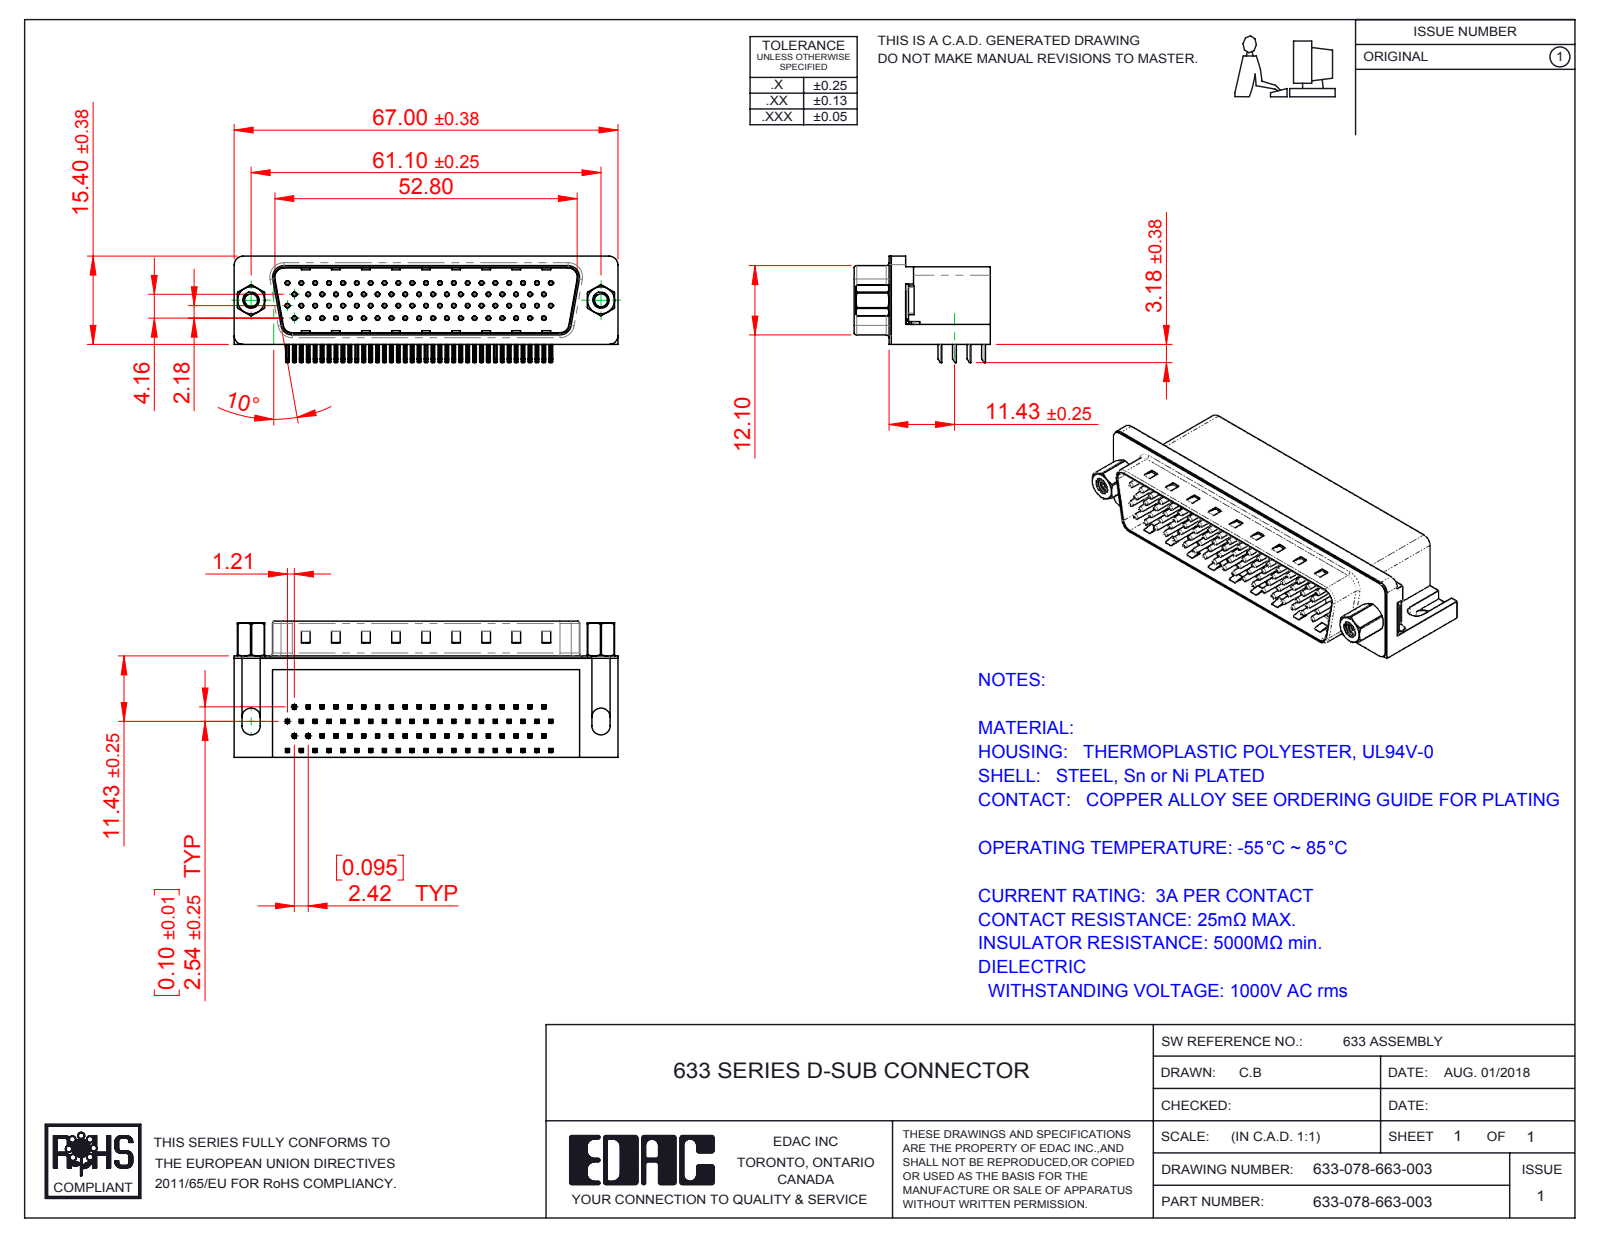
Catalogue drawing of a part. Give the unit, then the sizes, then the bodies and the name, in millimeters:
Units: millimetres
Overall size (bounding box): 67 × 23.8 × 18.58
Round holes (diameter × count): ⌀0.35 ×78, ⌀0.8 ×78, ⌀2.26 ×2, ⌀2.29 ×2, ⌀4 ×2, ⌀4.8 ×2, ⌀5 ×2
Round bosses / shafts (diameter × count): ⌀0.75 ×78, ⌀4.9 ×2, ⌀4.75 ×2, ⌀3.9 ×2, ⌀2.79 ×2
Partial cylindrical surfaces — rounded edges, fillets, slot ends (radius × count): R0.25 ×320, R0.12 ×156, R1 ×16, R0.5 ×9, R1.6 ×8, R1.5 ×6, R0.45 ×4, R0.9 ×4
Main face-to-face distances: 0.4, 13.2, 17.3, 11.7, 13.35, 2.05, 13.75, 1.65, 11.9, 1.85
Hole centre spacings: 2.42, 4.84, 7.26, 9.68, 6.26, 7.13, 12.1, 8.62
Volume: 14 767 mm³ · Surface area: 16 578 mm²
Bodies: 86 solids, 6390 faces (4001 planar, 1838 cylindrical, 551 other)
Part name (STEP PRODUCT): 633 Contact Top 78; 633 Non Board Mount_78 Contact; 633 Housing_78 Contact; 633 4-40 Threaded Rivet (+6 more)
STEP written by: SolidWorks 2016 (CONFIG_CONTROL_DESIGN)
